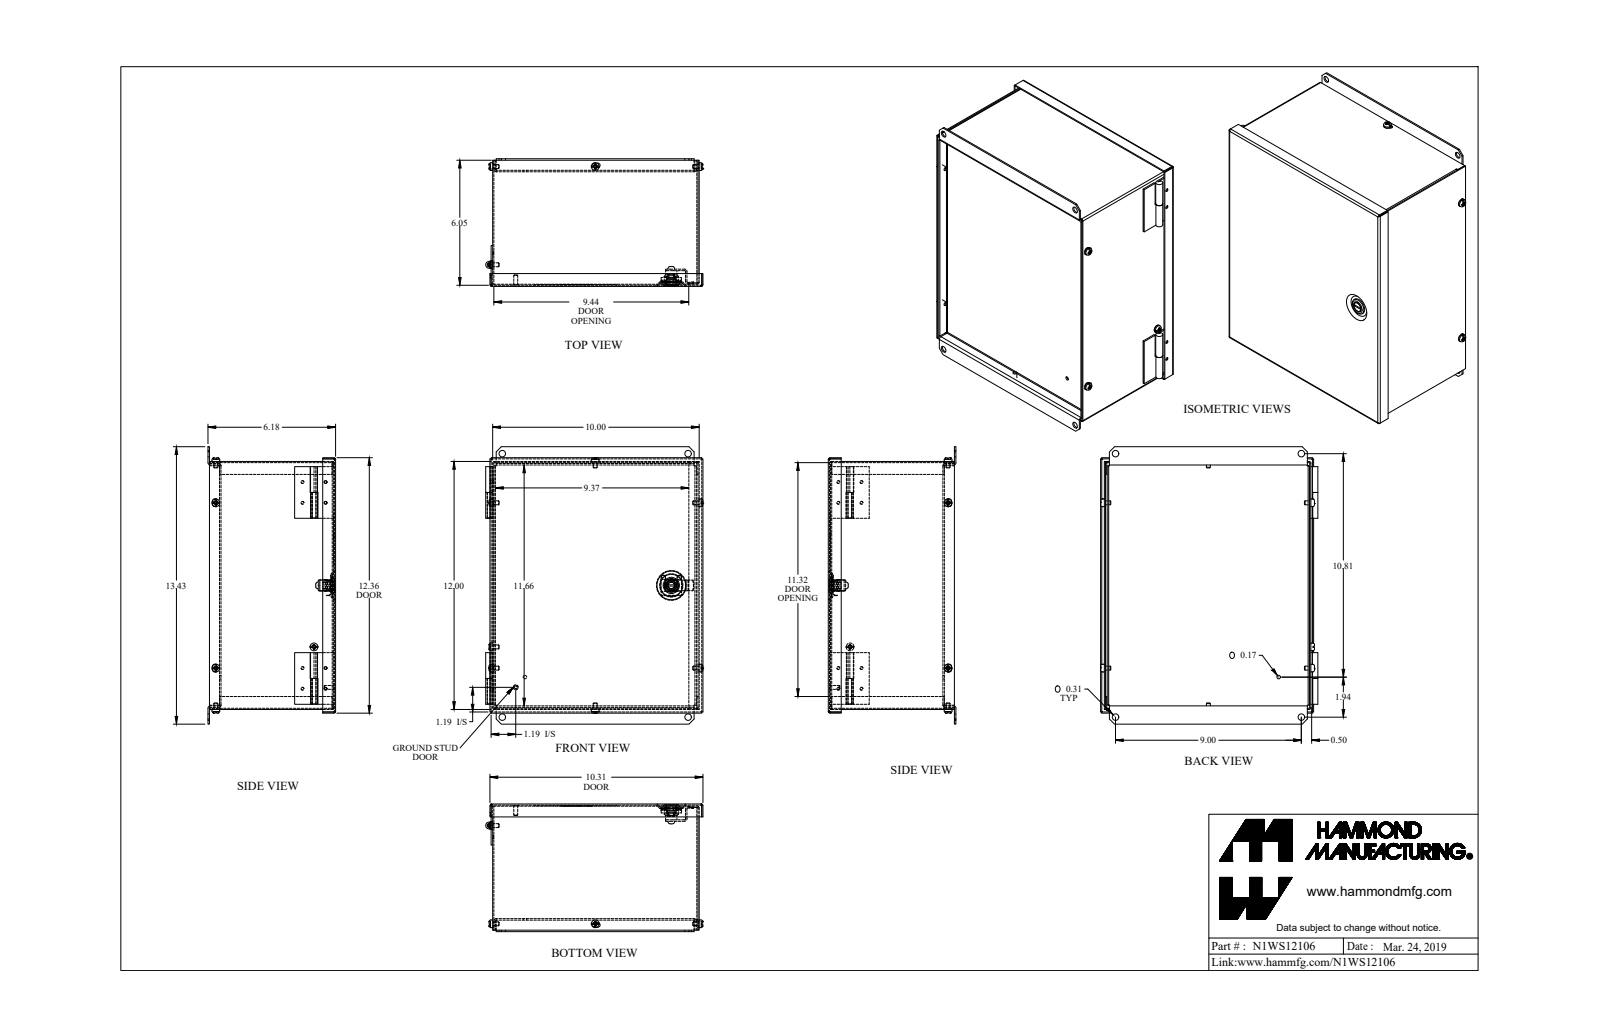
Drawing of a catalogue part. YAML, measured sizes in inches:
part_name: "N1WS12106"
step_written_by: "SolidWorks 2018 (AUTOMOTIVE_DESIGN)"
units: inches
bodies: {solids: 17, faces: 607, planar: 328, cylindrical: 214, other: 65}
overall_size: [13.425, 10.519, 6.179]
volume: 36.55
surface_area: 1203
round_holes:
  - {diameter: 0.14, count: 8}
  - {diameter: 0.17, count: 5}
  - {diameter: 0.312, count: 4}
  - {diameter: 0.187, count: 1}
  - {diameter: 0.319, count: 1}
  - {diameter: 0.476, count: 1}
round_bosses_or_shafts:
  - {diameter: 0.128, count: 8}
  - {diameter: 0.375, count: 4}
  - {diameter: 0.19, count: 4}
  - {diameter: 0.787, count: 1}
  - {diameter: 0.547, count: 1}
  - {diameter: 0.472, count: 1}
  - {diameter: 0.469, count: 1}
  - {diameter: 0.366, count: 1}
partial_cylinders:
  - {radius: 0.029, count: 9}
  - {radius: 0.086, count: 9}
  - {radius: 0.036, count: 8}
  - {radius: 0.108, count: 6}
  - {radius: 0.109, count: 6}
  - {radius: 0.012, count: 4}
  - {radius: 0.1, count: 4}
  - {radius: 0.079, count: 2}
face_to_face_distances: [0.057, 9.943, 0.072, 0.057, 11.943, 5.564, 5.621, 5.492, 5.549, 10]
hole_center_spacings: [9, 1, 1.119, 1.501, 9.069, 8, 4.195, 4.313]
